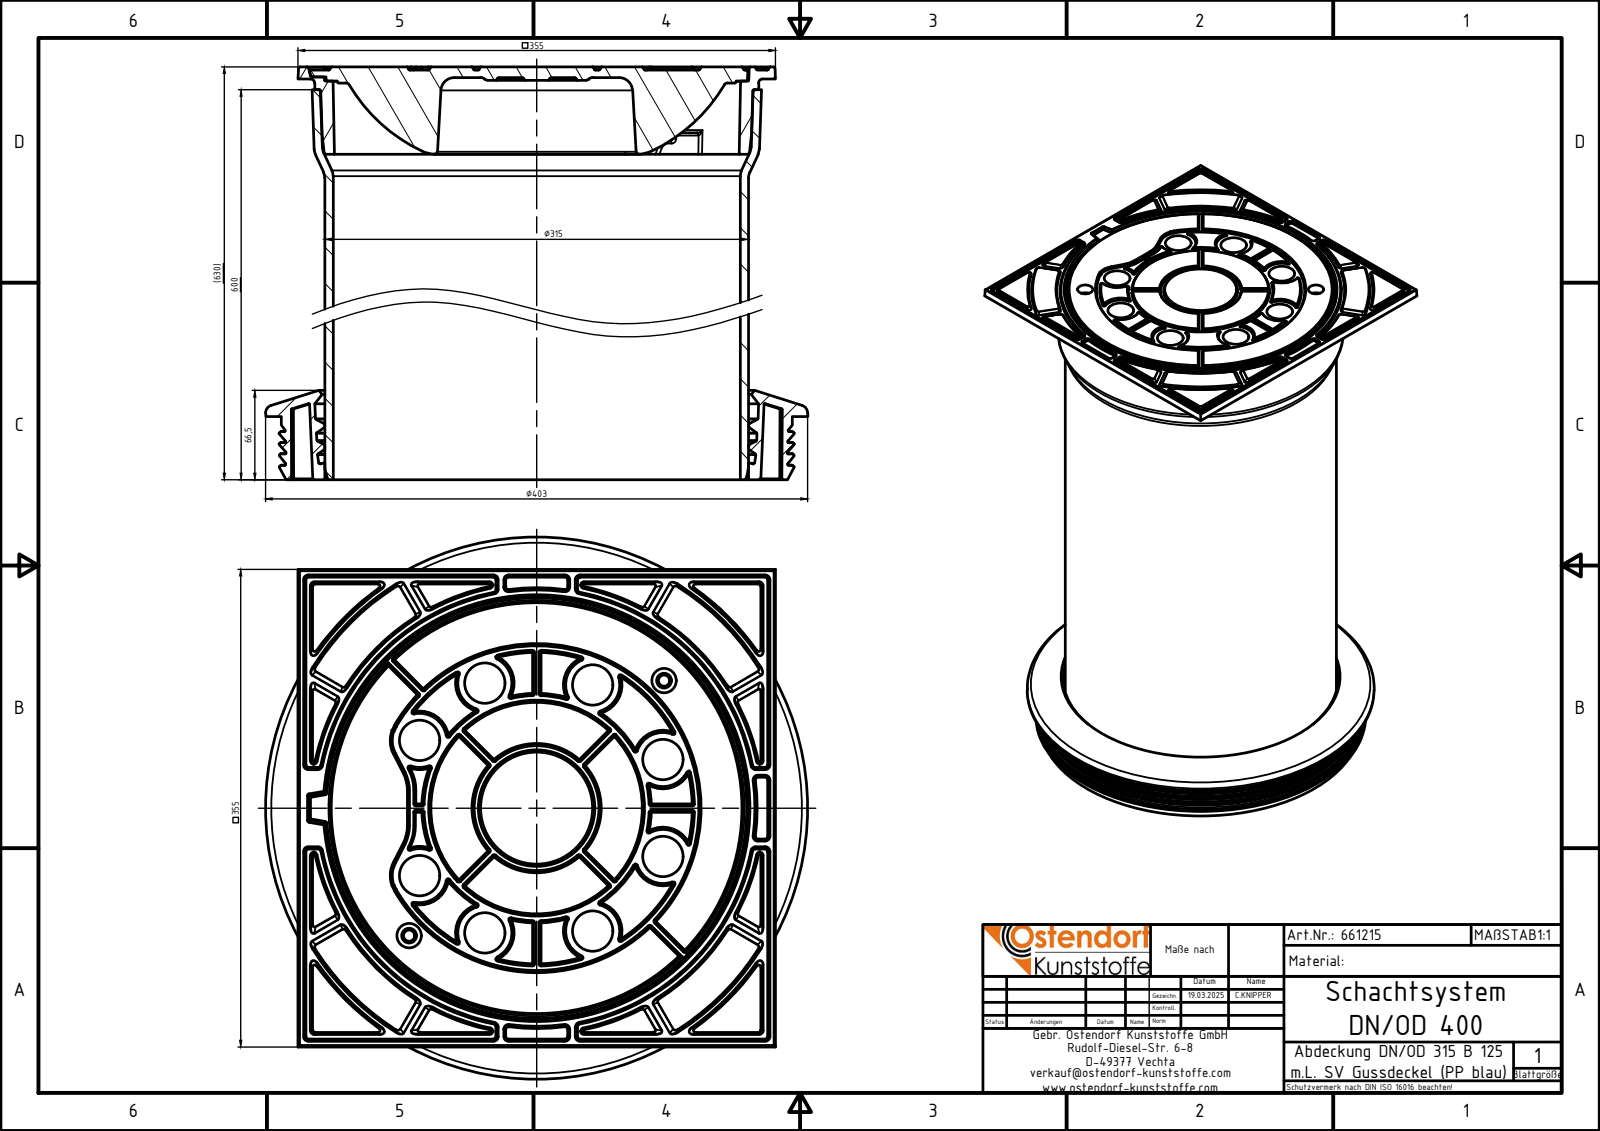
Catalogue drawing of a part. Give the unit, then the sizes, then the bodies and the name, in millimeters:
Units: millimetres
Overall size (bounding box): 617 × 403 × 403
Round holes (diameter × count): ⌀30 ×8, ⌀8.38 ×2, ⌀11 ×2, ⌀18 ×2, ⌀302.6 ×1, ⌀315 ×1
Round bosses / shafts (diameter × count): ⌀403 ×1, ⌀380 ×1, ⌀330 ×1
Partial cylindrical surfaces — rounded edges, fillets, slot ends (radius × count): R1 ×161, R2 ×8, R2.5 ×8
Main face-to-face distances: 9, 8, 2.5, 6.5, 608, 614.5, 617, 1.5, 47, 561
Hole centre spacings: 100.5, 64.61, 76.11, 80.14, 134, 135.14, 143.97, 151.12
Volume: 7 841 000 mm³ · Surface area: 2 067 000 mm²
Bodies: 4 solids, 1528 faces (200 planar, 257 cylindrical, 1071 other)
Part name (STEP PRODUCT): 661215z; 660205_Dichtungz; 660205_geändertz; 990000z (+2 more)
STEP written by: Autodesk Inventor 2024 (AUTOMOTIVE_DESIGN)
